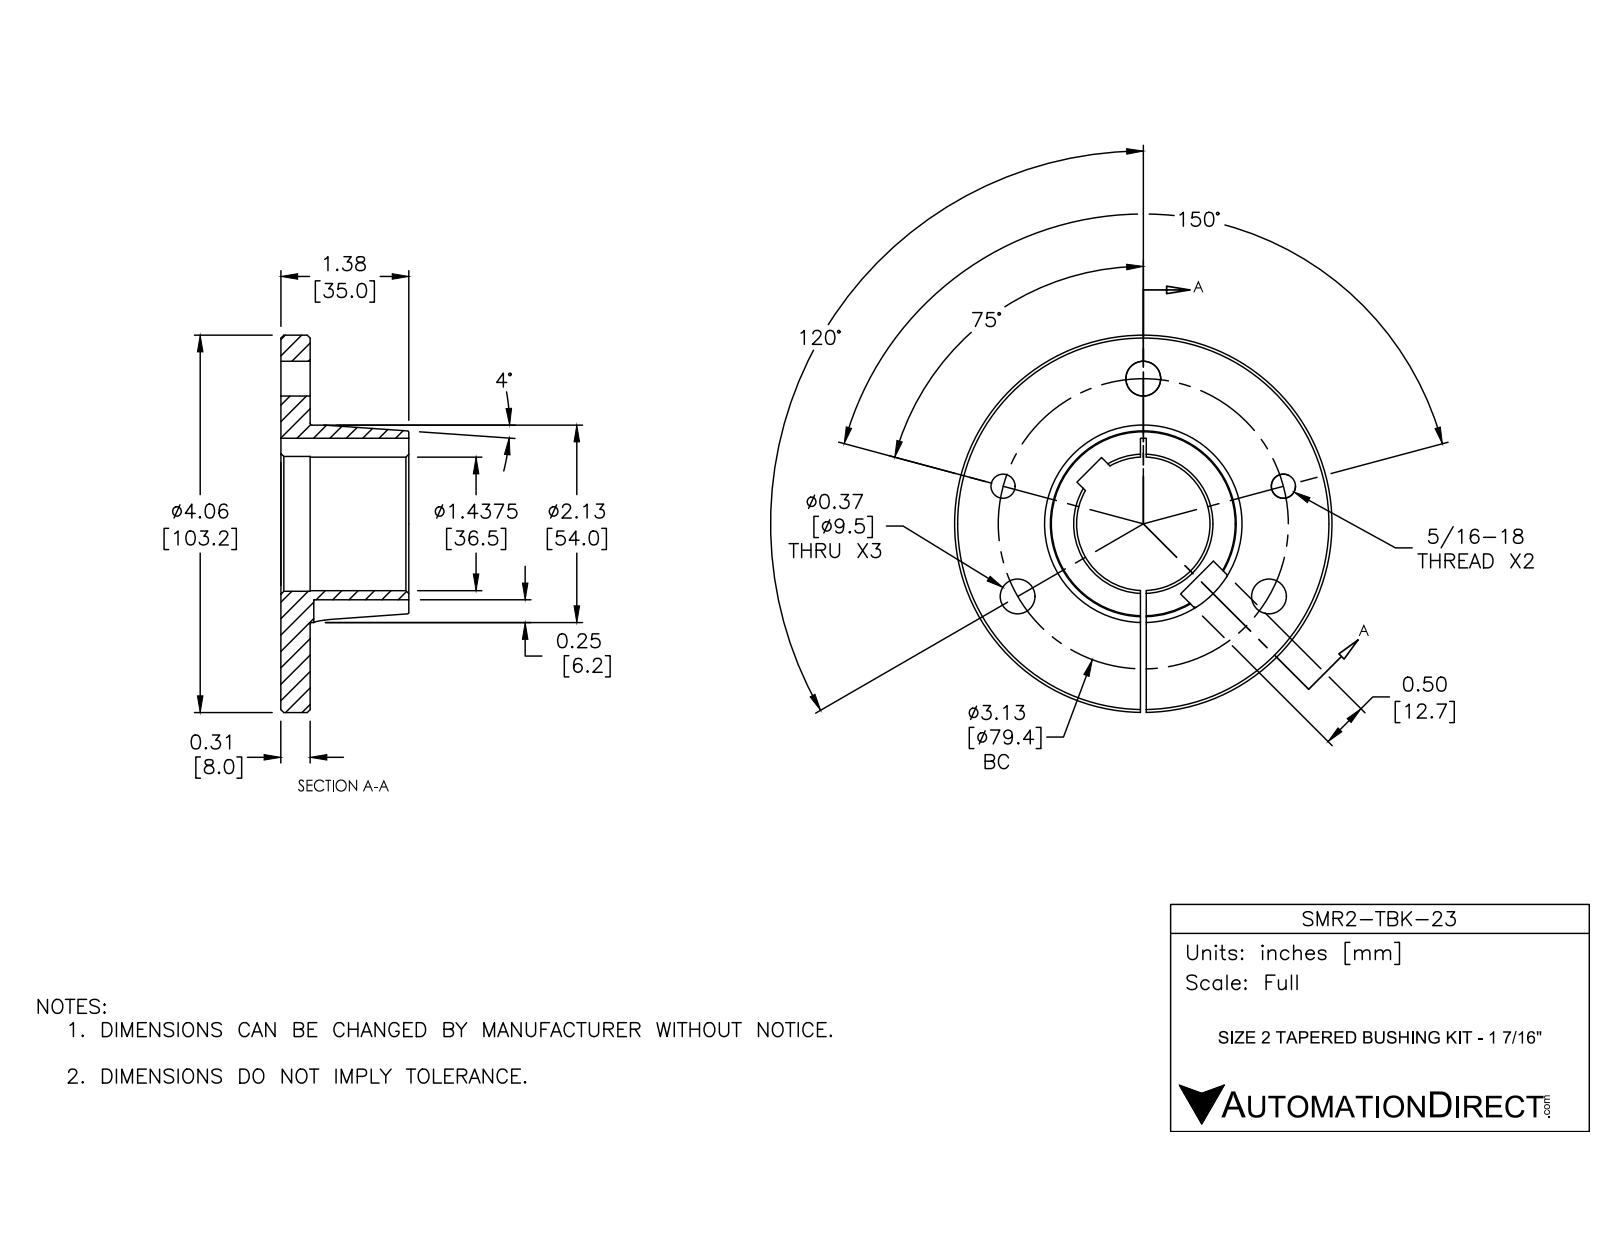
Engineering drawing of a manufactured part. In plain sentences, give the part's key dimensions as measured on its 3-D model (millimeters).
The part is named "SMR2-TBK-23". Its 3-D file was written by "SolidWorks 2016 (AUTOMOTIVE_DESIGN)". It is 1 solid with 124 faces: 18 planar, 79 cylindrical and 27 other. Overall it measures 103.2 by 103.2 by 35 millimeters. Its volume is 82 530 cubic millimeters and its surface area 27 220 square millimeters. Round holes: 3 of diameter 9.5, 2 of diameter 8.1, 1 of diameter 6.6, 1 of diameter 36.5, 1 of diameter 36.9. Round bosses or shafts: 1 of diameter 103.2, 1 of diameter 54. Partial cylindrical surfaces (rounded edges, fillets, slot ends): 2 of radius 3.3, 2 of radius 5. The main face-to-face distances are 8, 35, 27, 1.6, 41.7, 1.6, 11.1, 9.5, 12.7, 9. The hole center spacings are 39.7, 68.8, 30.4, 39.7, 39.7, 48.3, 48.4, 76.7.
